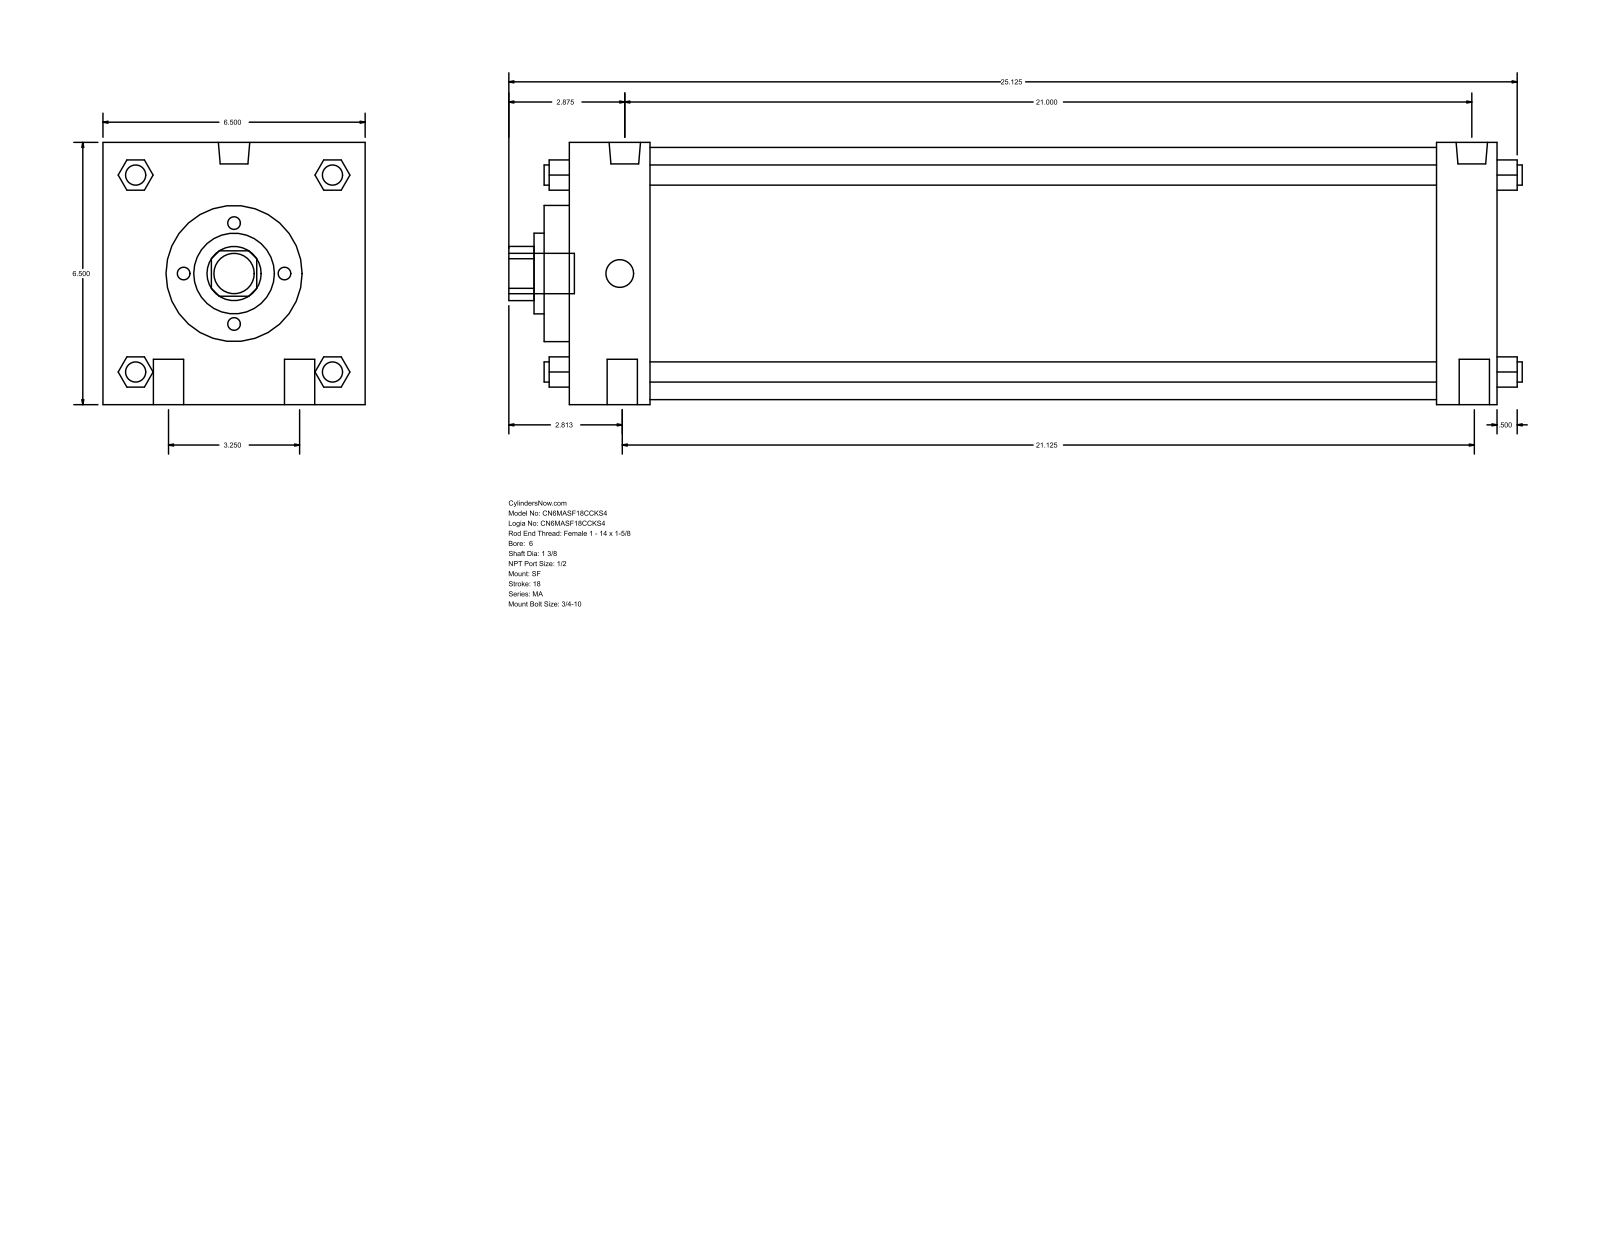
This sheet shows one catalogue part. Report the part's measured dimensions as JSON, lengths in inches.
{"part_name": "MA_SF__0600_1.375", "step_written_by": "GSSL Pune (CONFIG_CONTROL_DESIGN)", "units": "inches", "bodies": {"solids": 0, "faces": 126, "planar": 95, "cylindrical": 31, "other": 0}, "overall_size": [25.125, 6.5, 6.5], "round_holes": [[1.375, 1], [2, 1], [3.375, 1], [6.25, 1]], "round_bosses_or_shafts": [[0.75, 4], [0.5, 4], [0.778, 2], [0.687, 2], [1, 1]], "partial_cylinders_radius": [[0.672, 1]], "face_to_face_distances": [6.5, 23, 21.5, 2, 1.5, 19.5, 21, 0.625, 23.625, 2.625]}
